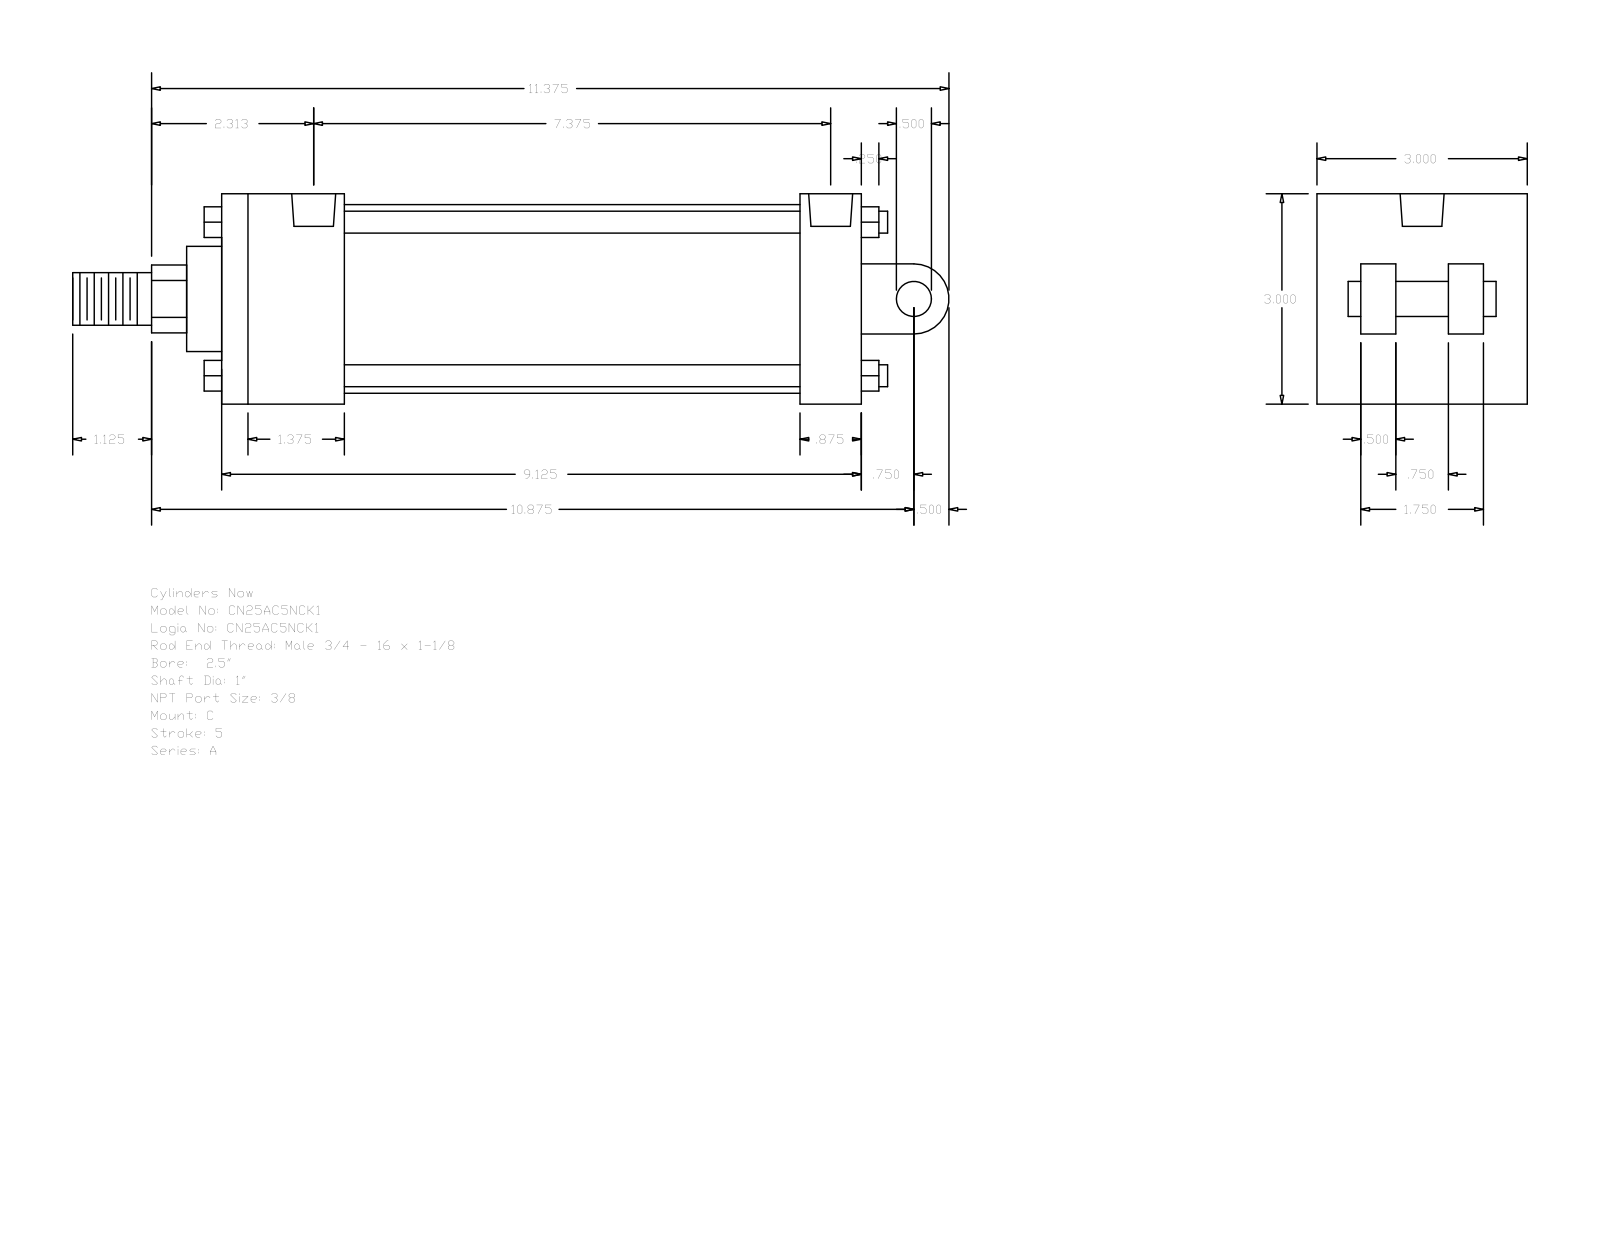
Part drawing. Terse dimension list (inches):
name: A_C__0250_1
written by: GSSL Pune (CONFIG_CONTROL_DESIGN)
unit: in
bodies: 0 solids, 135 faces (102 planar, 33 cylindrical, 0 other)
size: 12.5 × 3 × 3
holes: 4× ⌀0.219, 2× ⌀0.627
bosses: 4× ⌀0.313, 1× ⌀2.69, 1× ⌀1.5, 1× ⌀1, 1× ⌀0.75, 1× ⌀0.5
rounds: 1× R0.484, 1× R0.5
face distances: 3, 9.125, 0.5, 1.75, 8.25, 6.5, 7.375, 0.875, 0.625, 1
hole spacings: 0.094, 7.469, 7.562, 7.375
